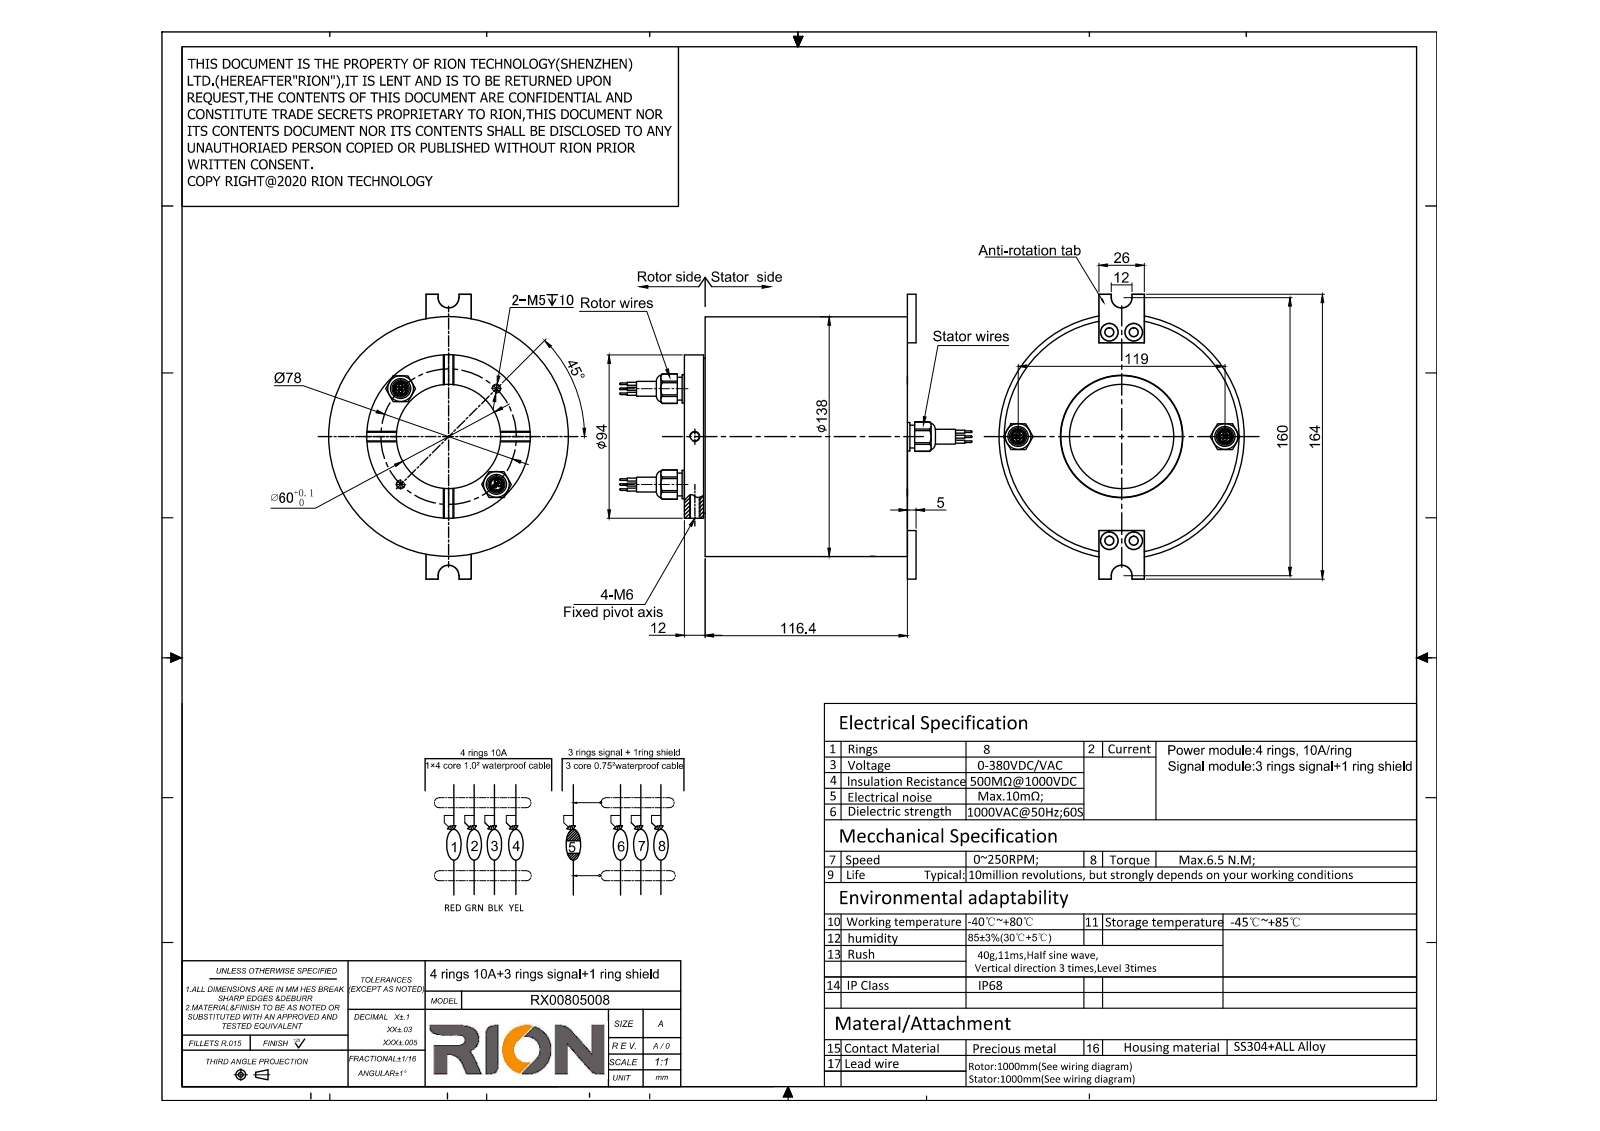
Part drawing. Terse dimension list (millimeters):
name: RX00805008
written by: SolidWorks 2014 (CONFIG_CONTROL_DESIGN)
unit: mm
bodies: 1 solid, 178 faces (92 planar, 58 cylindrical, 28 other)
size: 186 × 164 × 138
volume: 1 476 000 mm³; area: 112 725 mm²
holes: 4× ⌀5.2, 2× ⌀4.2, 2× ⌀5, 1× ⌀60, 1× ⌀70
bosses: 4× ⌀15, 4× ⌀13.1, 3× ⌀5, 1× ⌀138, 1× ⌀94, 1× ⌀89, 1× ⌀69.8, 1× ⌀5.43
rounds: 2× R6
face distances: 116.4, 12, 128.4, 133.4, 121.4, 5, 14.85, 11, 1, 117.4
hole spacings: 60.41, 14, 38.4, 39, 47.4, 89.97, 94.16, 120
